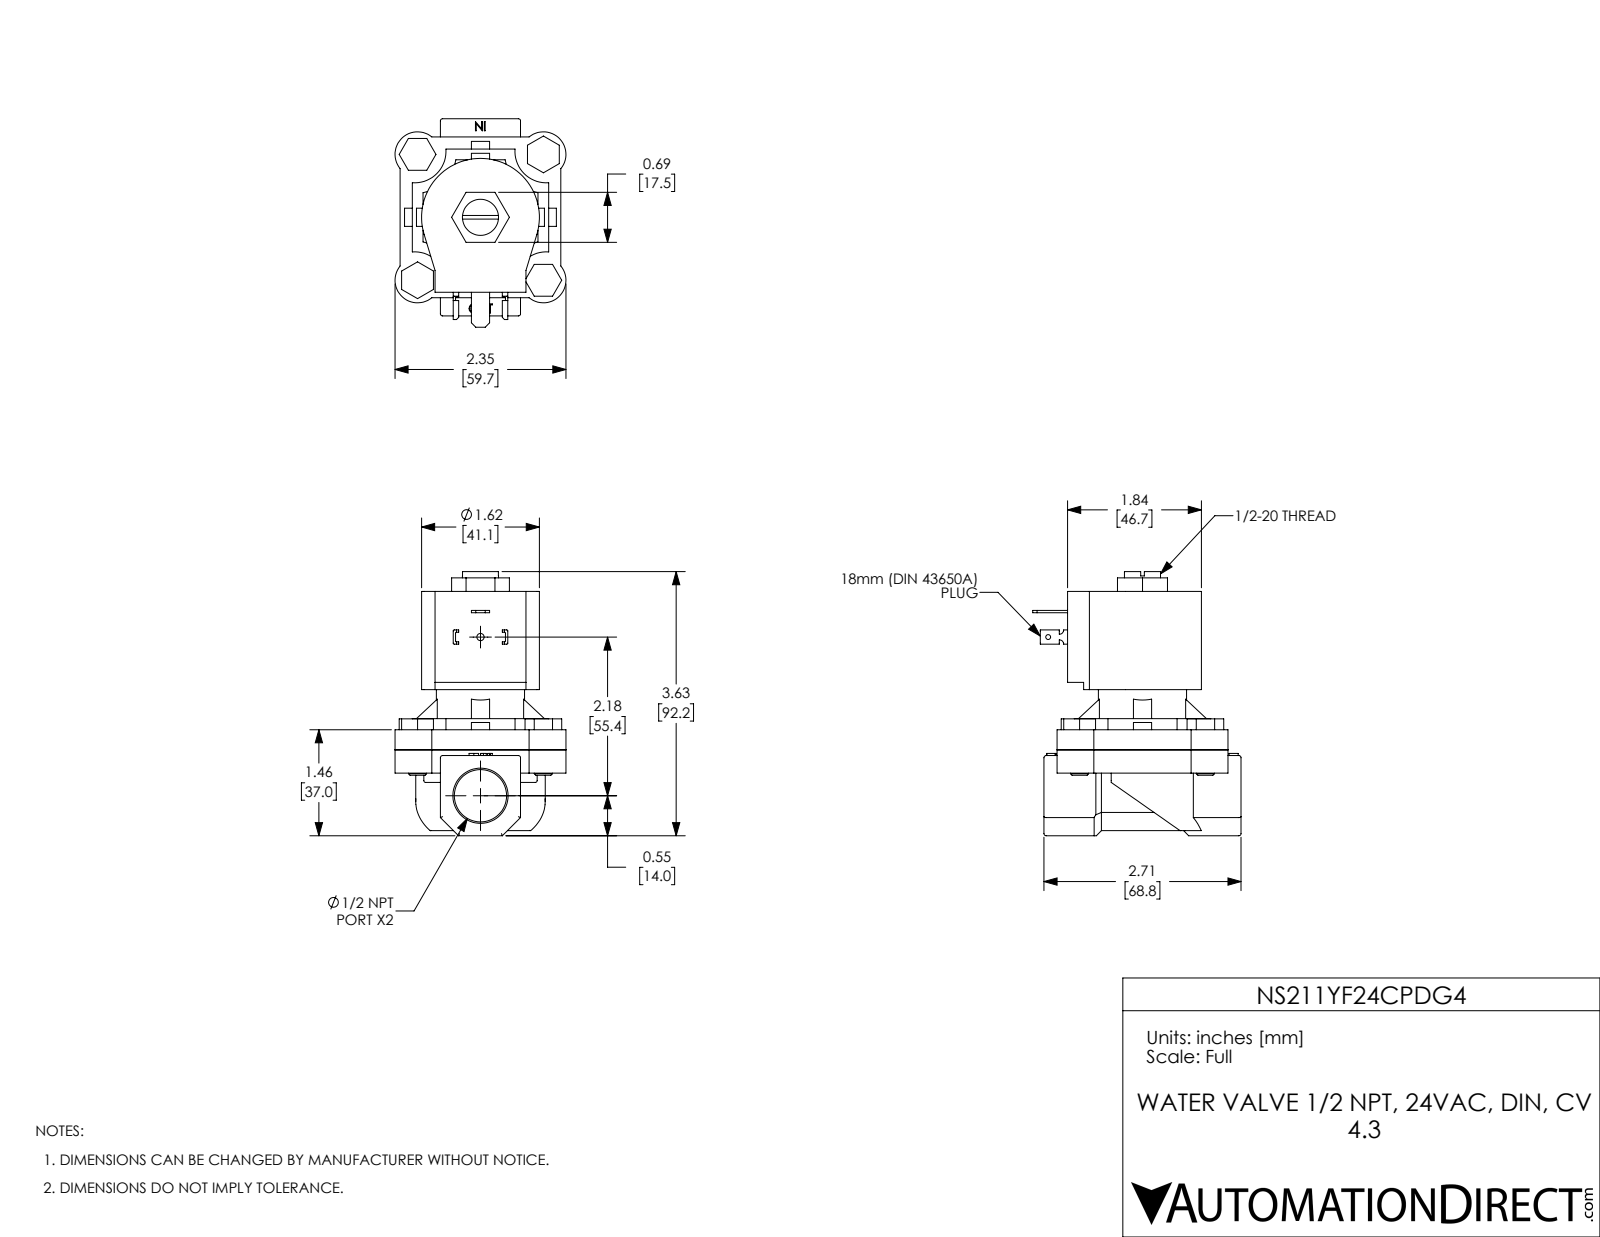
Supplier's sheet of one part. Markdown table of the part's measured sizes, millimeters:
| quantity | value |
| --- | --- |
| part name | NS211YF24CPDG4 |
| STEP written by | SolidWorks 2021 (CONFIG_CONTROL_DESIGN) |
| units | millimeters |
| bodies | 11 solids, 385 faces (239 planar, 113 cylindrical, 33 other) |
| overall size | 92.2 × 72.8 × 59.7 |
| volume | 155 200 mm³ |
| surface area | 42 030 mm² |
| round holes (diameter × count) | 6.4 × 4, 1.7 × 1, 2.5 × 1, 12.6 × 1, 13 × 1, 18.3 × 1, 29.3 × 1 |
| round bosses / shafts (diameter × count) | 6.3 × 4, 30.8 × 1 |
| partial cylindrical surfaces (radius × count) | 0.8 × 15, 0.4 × 8, 7.9 × 4, 11 × 4, 14.7 × 4, 1.5 × 2, 20.6 × 1, 22.6 × 1 |
| main face-to-face distances | 7, 55.3, 48.3, 8.1, 15.1, 63.4, 14.1, 42.1, 6.4, 29.1 |
| hole center spacings | 31.1, 43.9, 62.1, 55.4 |
